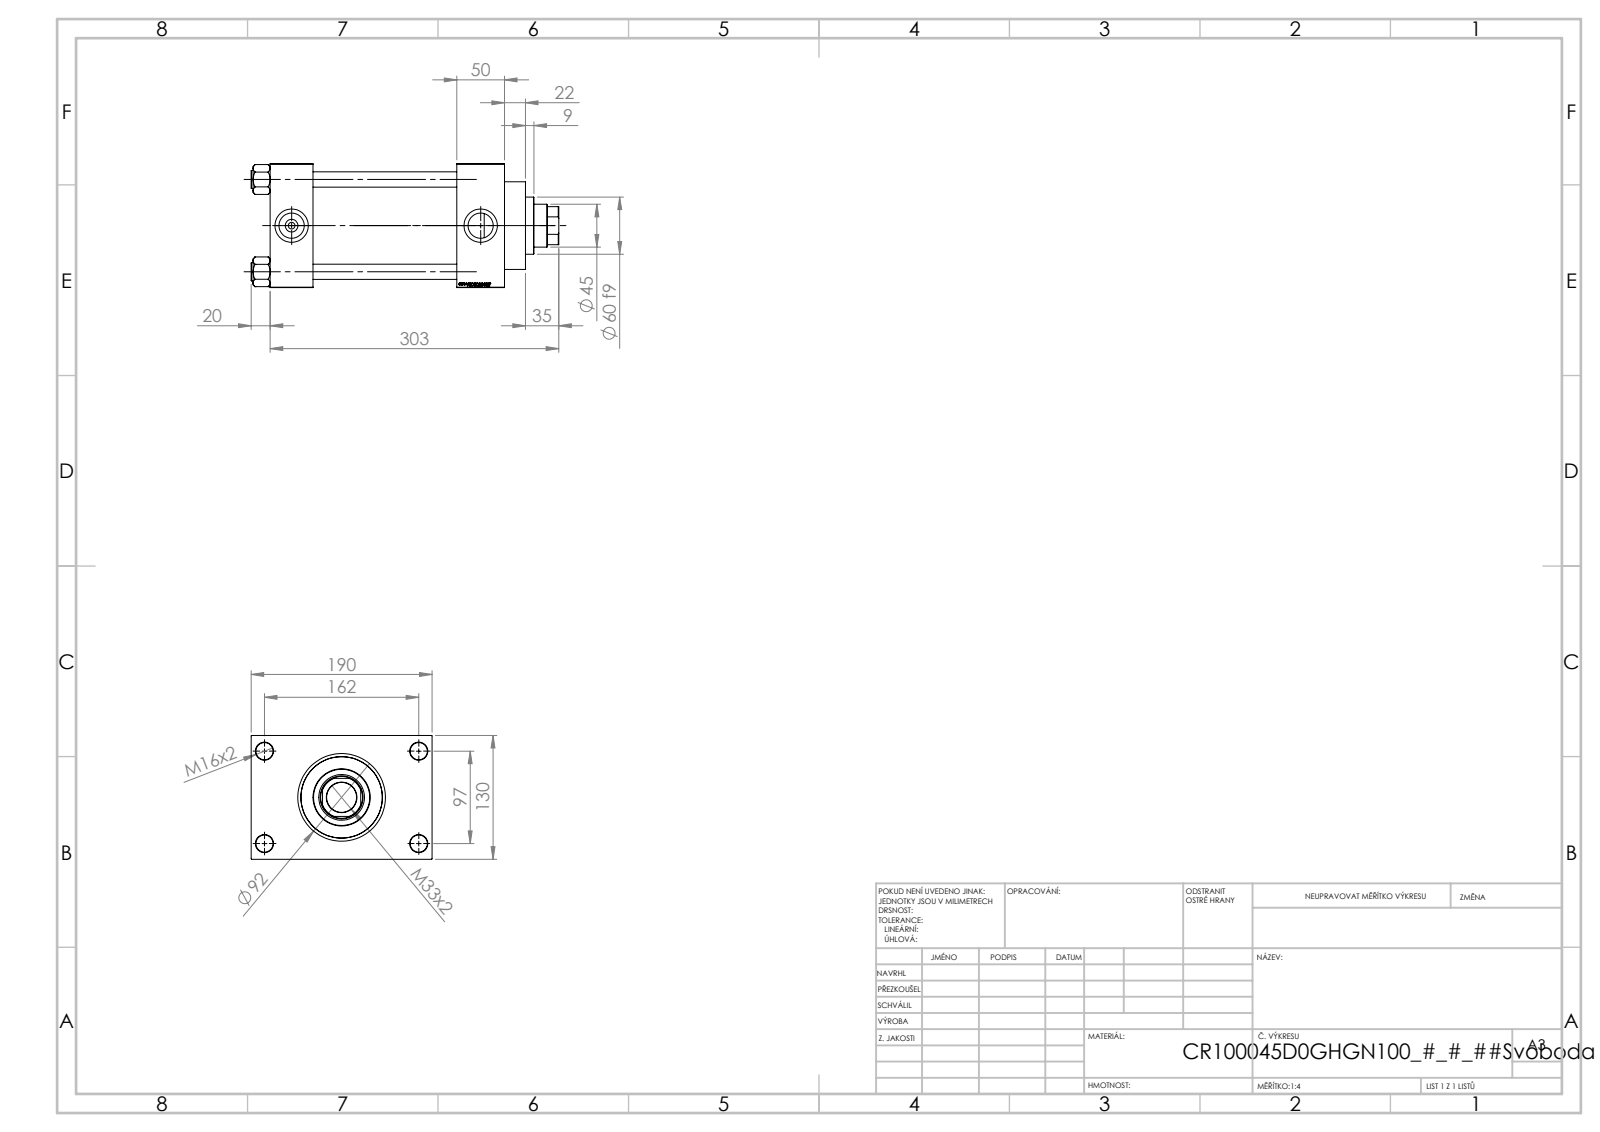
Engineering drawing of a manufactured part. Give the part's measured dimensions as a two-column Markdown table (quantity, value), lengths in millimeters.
| quantity | value |
| --- | --- |
| part name | V215CR_D_Body; V215CR_D_TYCINKA; V215_VC_A; NUT_M5_D (+1 more) |
| STEP written by | SolidWorks 2019 (CONFIG_CONTROL_DESIGN) |
| units | millimeters |
| bodies | 11 solids, 1151 faces (545 planar, 88 cylindrical, 518 other) |
| overall size | 323 × 190 × 130 |
| volume | 2 860 000 mm³ |
| surface area | 434 045 mm² |
| round holes (diameter × count) | 16 × 4, 18 × 4, 7 × 2, 26.44 × 2, 35 × 2, 31.5 × 1, 45 × 1, 48 × 1, 76 × 1, 85.5 × 1, 100 × 1 |
| round bosses / shafts (diameter × count) | 19 × 4, 106 × 1, 92 × 1, 60 × 1 |
| partial cylindrical surfaces (radius × count) | 22 × 1 |
| main face-to-face distances | 130, 45, 196, 151, 246, 201, 50, 30, 160, 96 |
| hole center spacings | 32.55, 68.52, 94.41, 96.9, 102.27, 129.45, 161.73, 97 |
